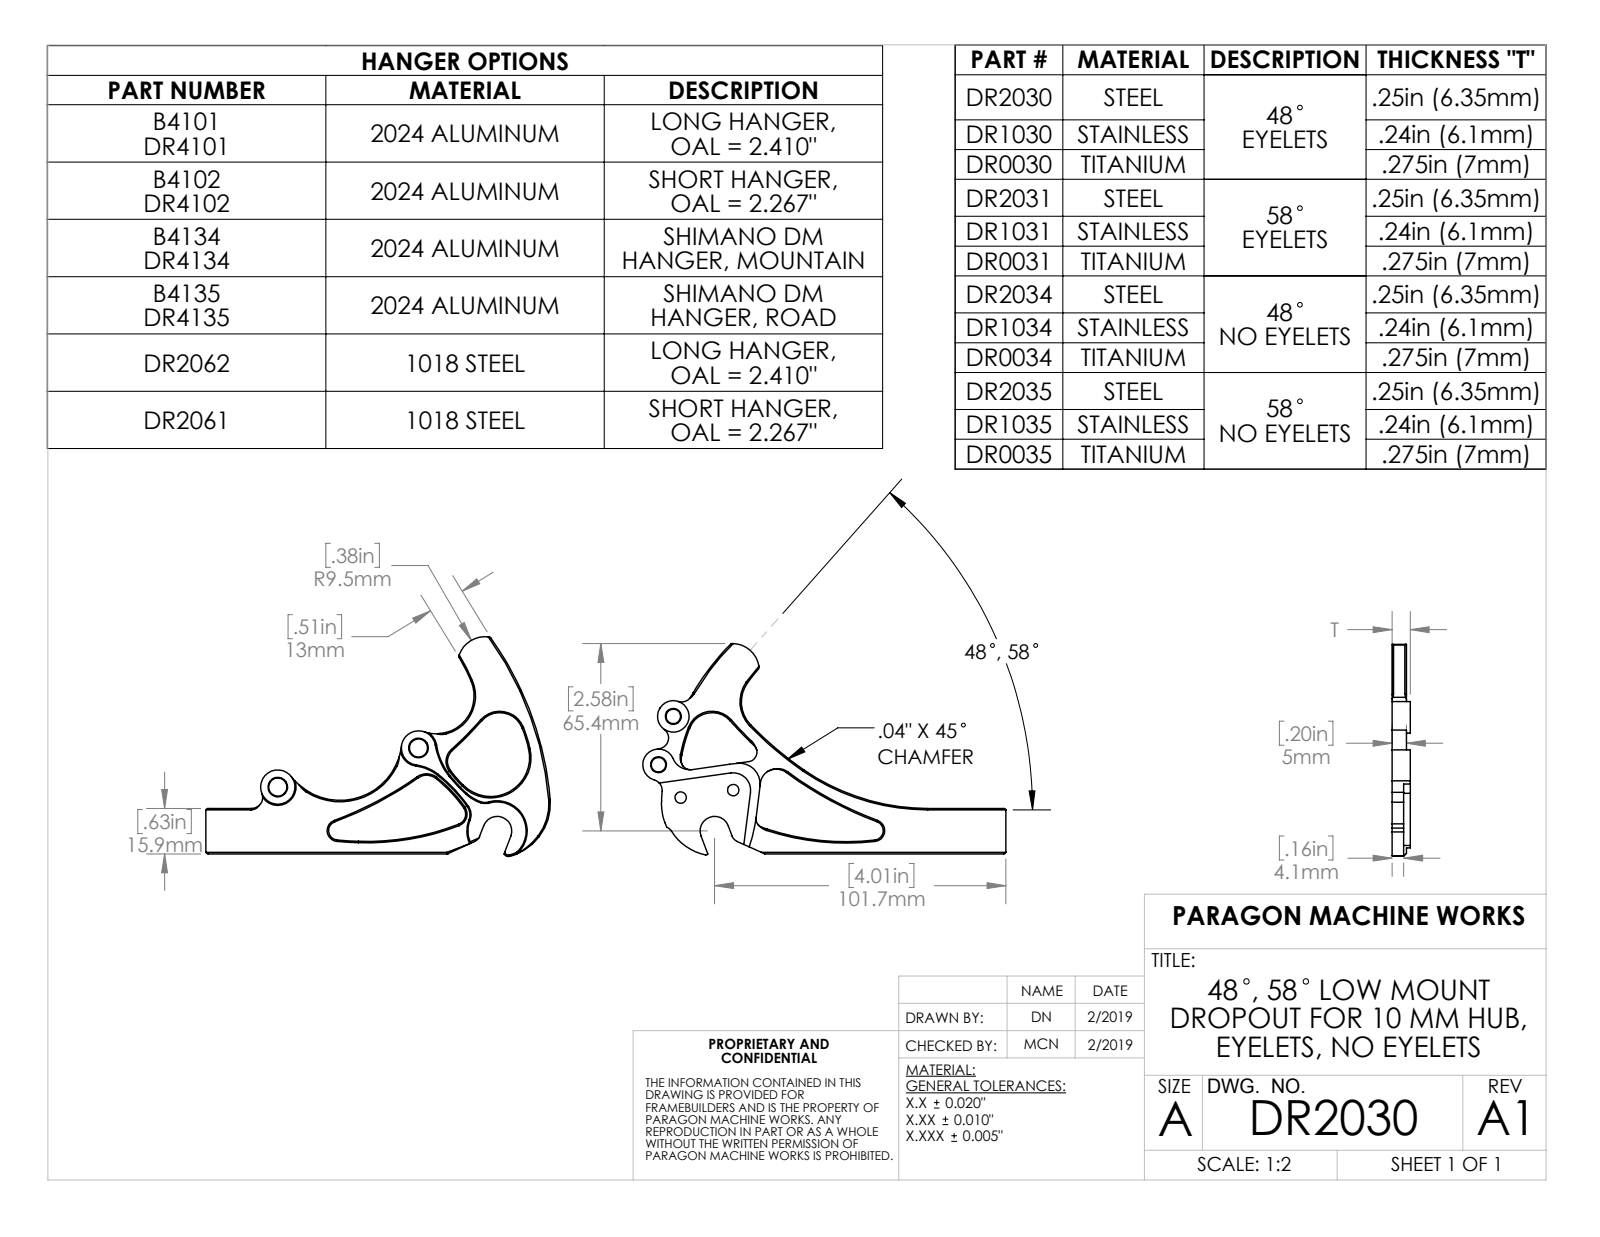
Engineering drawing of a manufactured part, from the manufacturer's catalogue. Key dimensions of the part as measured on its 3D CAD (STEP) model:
Part name (STEP PRODUCT): DR2030; DR2030R; DR2030L
STEP written by: SolidWorks 2015 (AUTOMOTIVE_DESIGN)
Units: inches
Bodies: 2 solids, 288 faces (46 planar, 116 cylindrical, 126 other)
Overall size (bounding box): 11 × 2.928 × 0.25
Volume: 1.691 in³ · Surface area: 27.23 in²
Round holes (diameter × count): ⌀0.2 ×4, ⌀0.157 ×2, ⌀0.25 ×2
Round bosses / shafts (diameter × count): ⌀0.434 ×3, ⌀0.472 ×1
Partial cylindrical surfaces — rounded edges, fillets, slot ends (radius × count): R0.03 ×9, R0.15 ×8, R0.13 ×6, R0.2 ×5, R0.016 ×2, R0.125 ×2, R0.204 ×2, R0.33 ×2
Main face-to-face distances: 0.197, 0.053, 0.25, 0.16, 0.107, 0.09, 0.625, 11, 0.12, 0.553
Hole centre spacings: 0.695, 1.778, 0.544, 0.73, 1.085, 1.12, 1.306, 1.446
